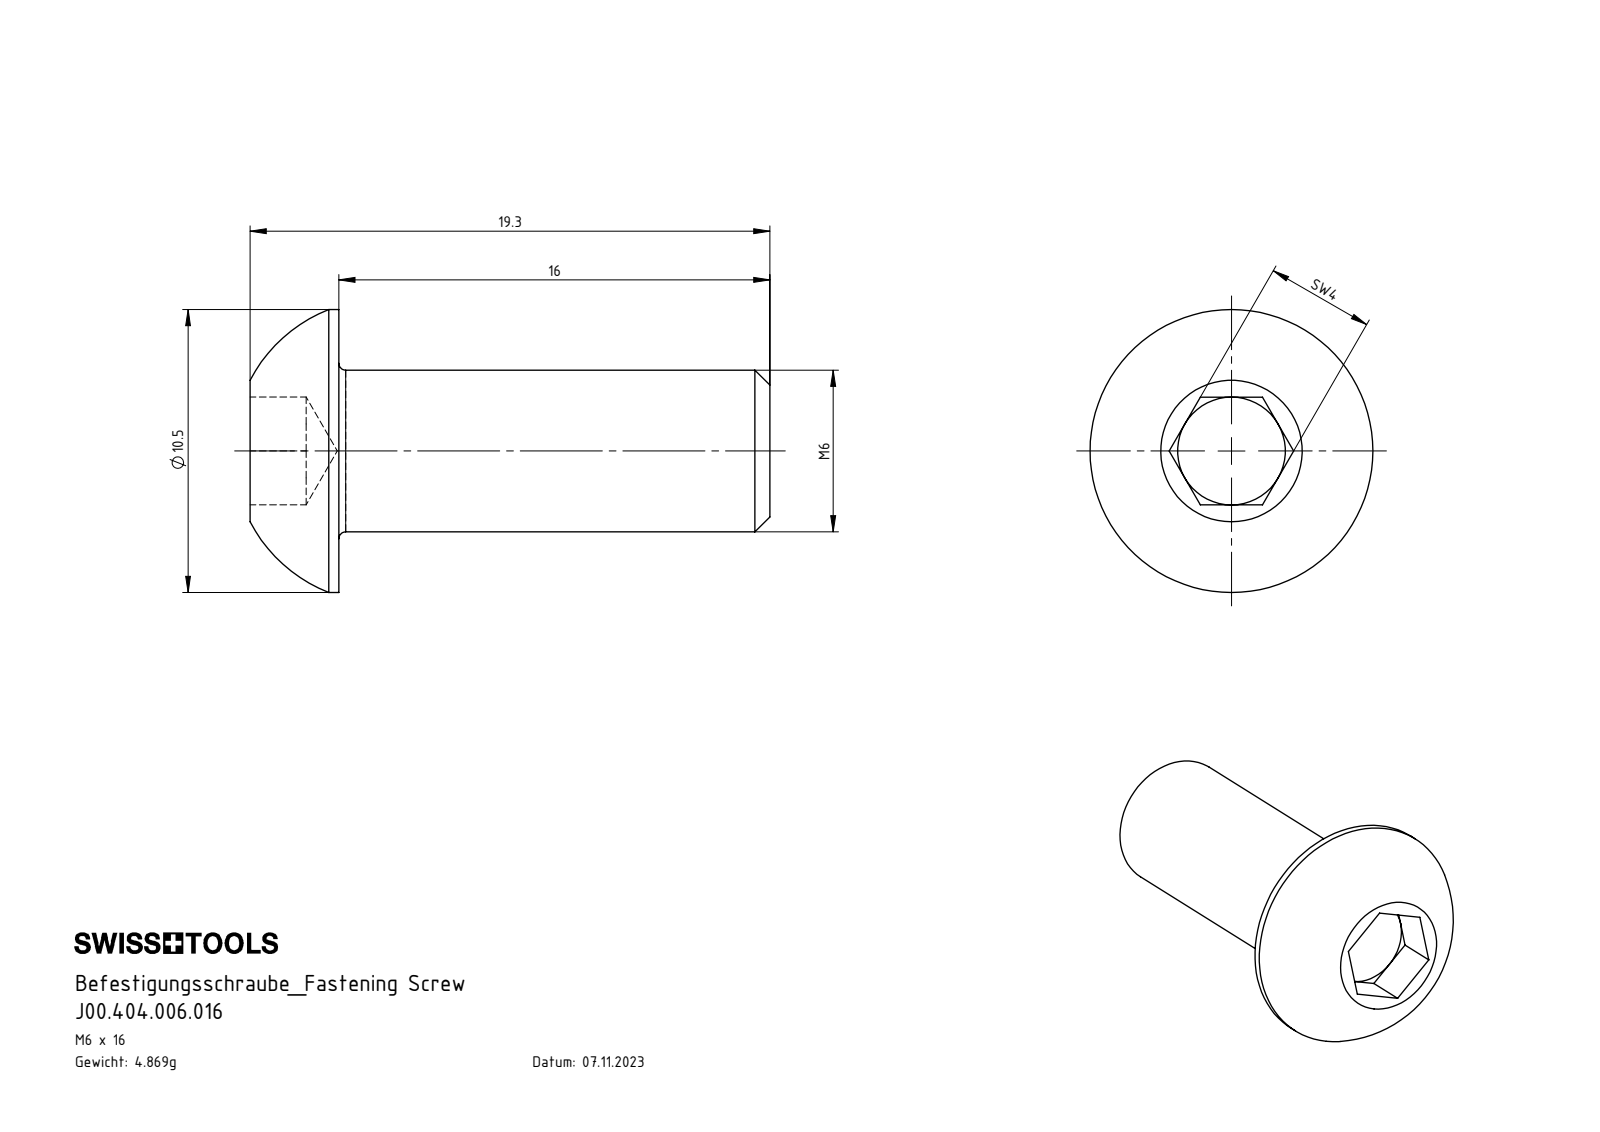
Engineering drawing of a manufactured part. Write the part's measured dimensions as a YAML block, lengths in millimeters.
part_name: "J00.404.006.016"
step_written_by: "SolidWorks 2022 (AUTOMOTIVE_DESIGN)"
units: millimeters
bodies: {solids: 1, faces: 27, planar: 15, cylindrical: 4, other: 8}
overall_size: [19.3, 10.5, 10.5]
volume: 620
surface_area: 548
round_bosses_or_shafts:
  - {diameter: 10.5, count: 1}
  - {diameter: 6, count: 1}
face_to_face_distances: [16, 4, 3.3, 19.3, 2.08, 1.22, 17.22]
